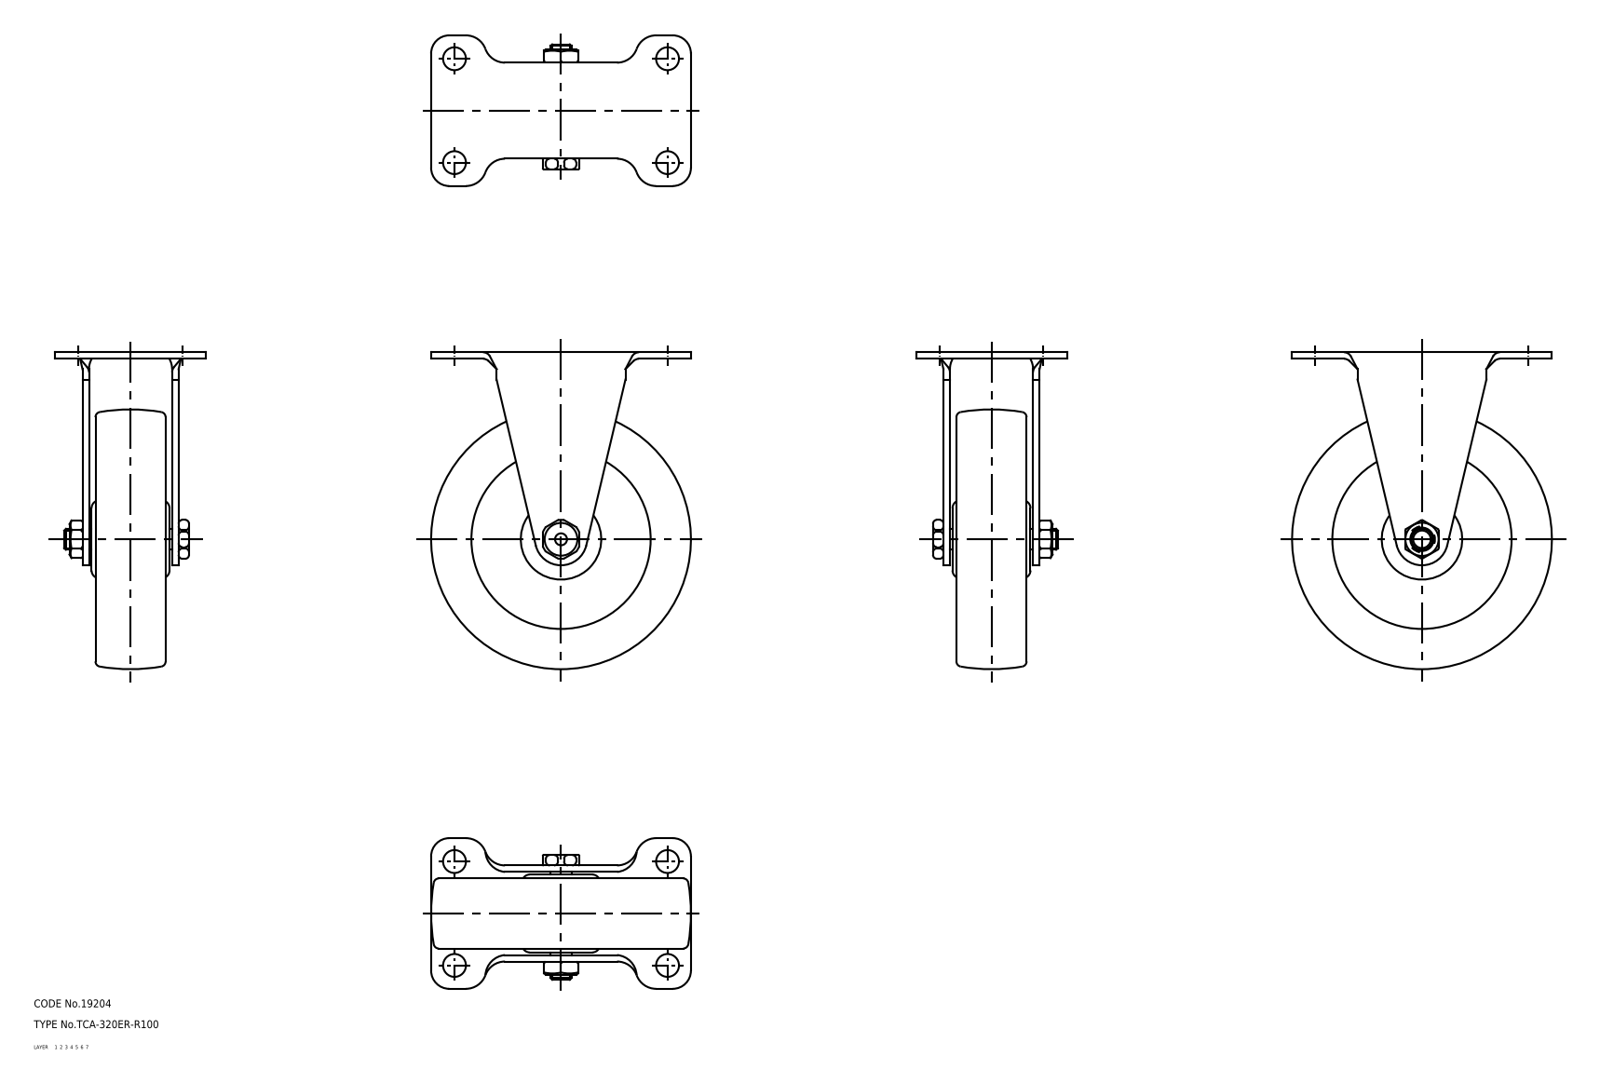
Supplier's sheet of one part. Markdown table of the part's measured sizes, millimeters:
| quantity | value |
| --- | --- |
| part name | wheel; axle; 320ER_R100_3185_36 |
| STEP written by | CADfix (AUTOMOTIVE_DESIGN) |
| units | millimeters |
| bodies | 3 solids, 161 faces (0 planar, 0 cylindrical, 161 other) |
| overall size | 122 × 100 × 58 |
| volume | 229 533 mm³ |
| surface area | 46 938 mm² |
